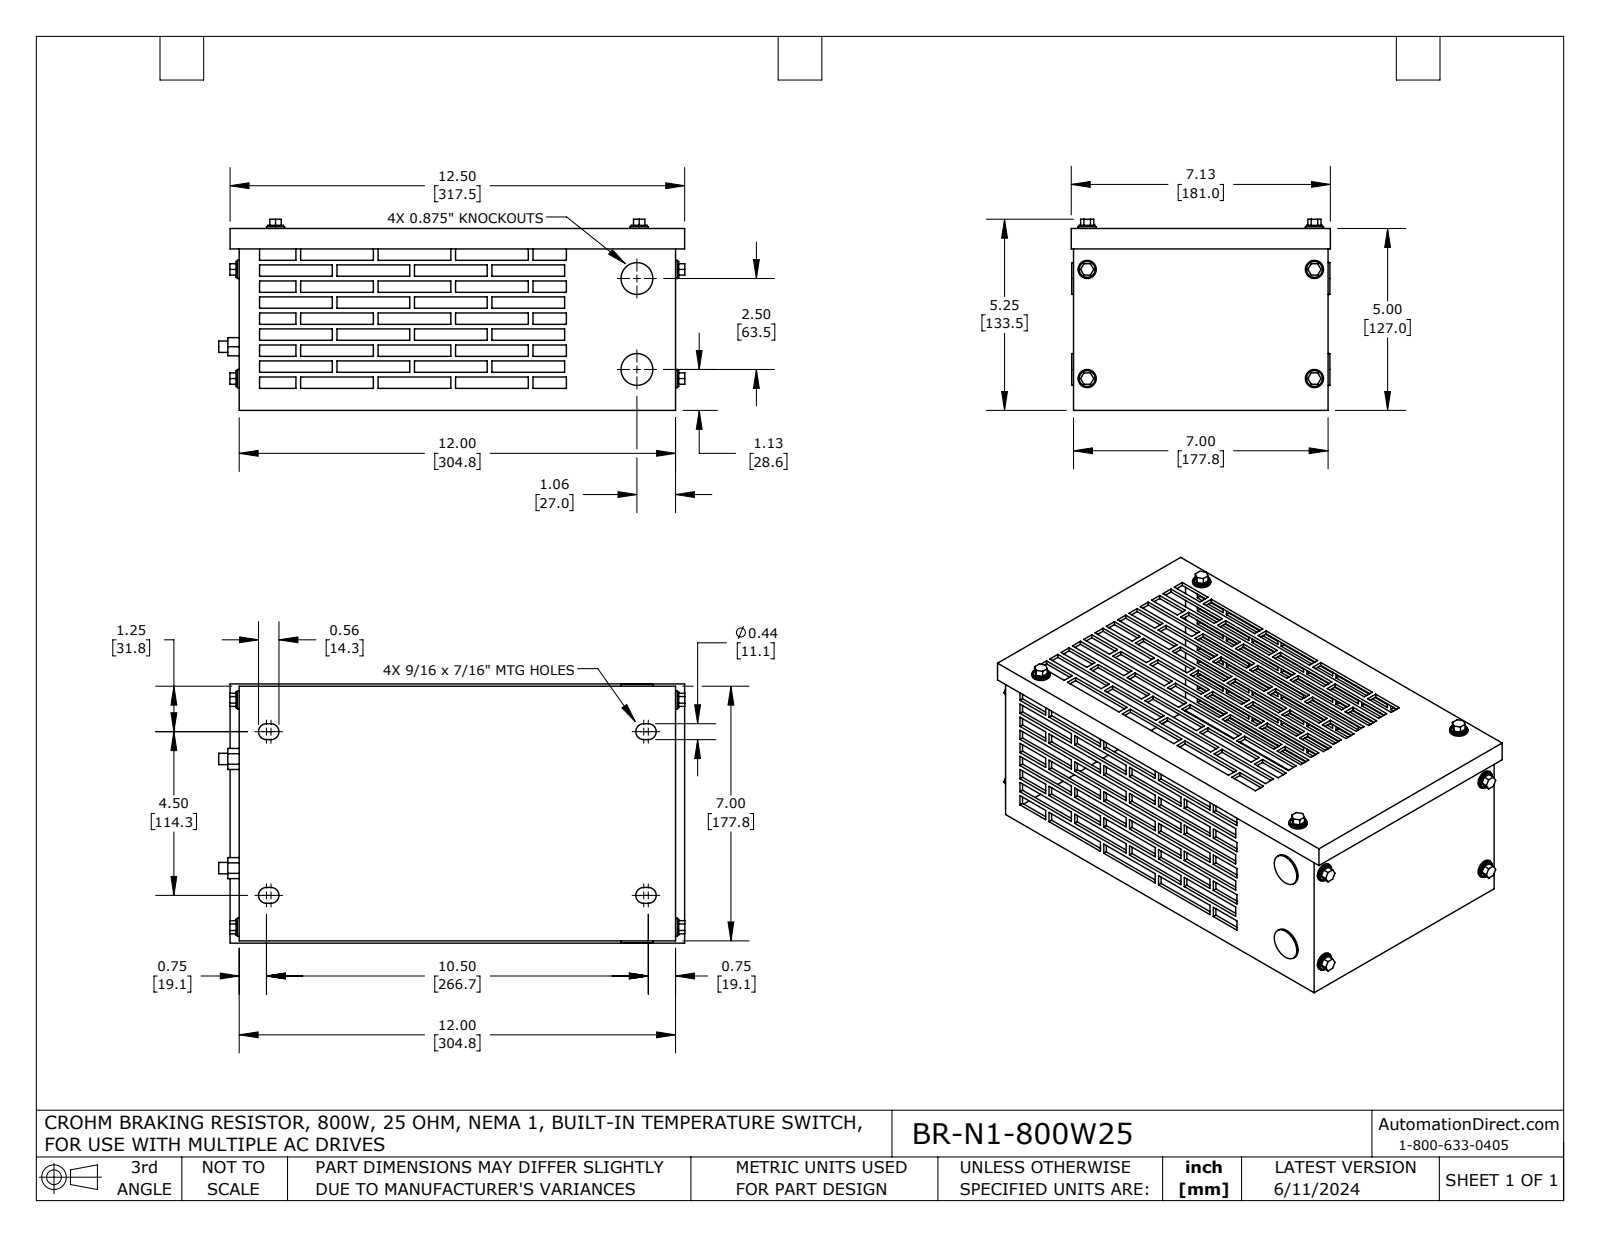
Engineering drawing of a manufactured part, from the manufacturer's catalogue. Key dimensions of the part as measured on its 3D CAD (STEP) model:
Part name (STEP PRODUCT): BR-N1-800W25
STEP written by: SolidWorks 2021 (AUTOMOTIVE_DESIGN)
Units: inches
Bodies: 31 solids, 846 faces (746 planar, 100 cylindrical, 0 other)
Overall size (bounding box): 12.817 × 7.125 × 5.254
Volume: 28.59 in³ · Surface area: 639.2 in²
Round holes (diameter × count): ⌀0.25 ×8, ⌀0.75 ×2
Round bosses / shafts (diameter × count): ⌀0.5 ×8, ⌀0.437 ×8, ⌀0.875 ×2, ⌀0.313 ×2
Partial cylindrical surfaces — rounded edges, fillets, slot ends (radius × count): R0.219 ×8
Main face-to-face distances: 0.1, 4.9, 11.9, 6.9, 5, 4.8, 12, 7, 11.8, 6.8
Hole centre spacings: 6.25, 3, 6.933, 10, 11.793, 2.5
